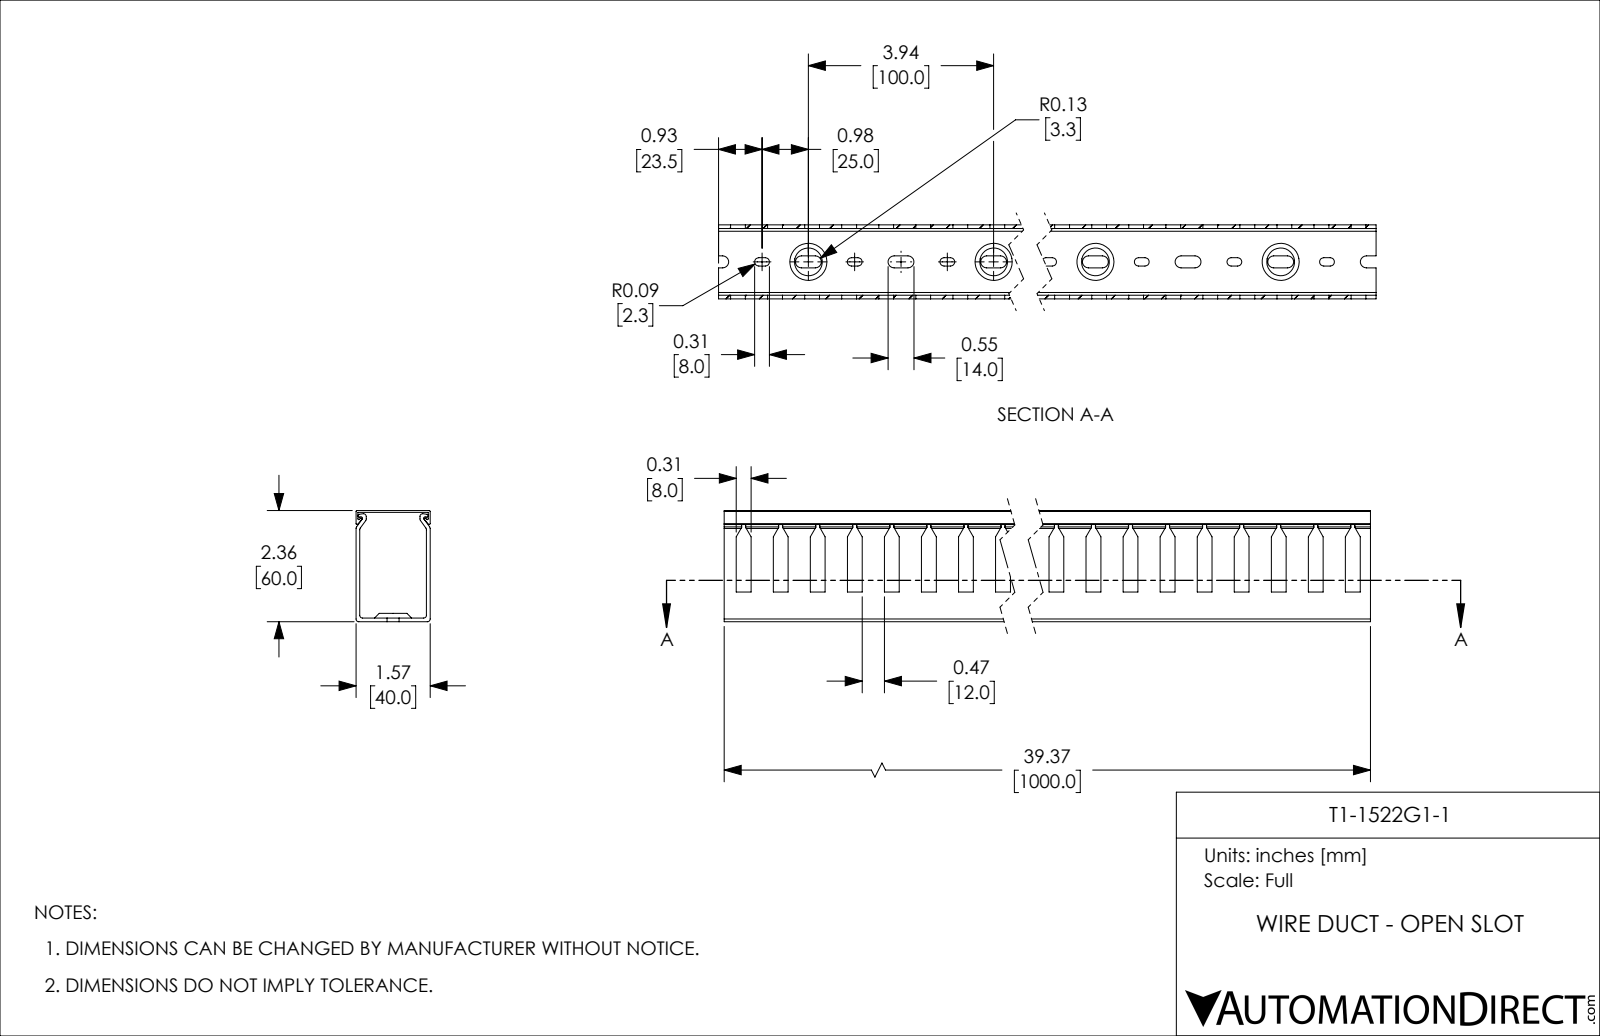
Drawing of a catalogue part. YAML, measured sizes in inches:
part_name: "T1-1522G1-1"
step_written_by: "SolidWorks 2021 (CONFIG_CONTROL_DESIGN)"
units: inches
bodies: {solids: 2, faces: 775, planar: 444, cylindrical: 311, other: 20}
overall_size: [39.37, 2.362, 1.575]
volume: 22.1
surface_area: 654.8
partial_cylinders:
  - {radius: 0.089, count: 40}
  - {radius: 0.128, count: 40}
  - {radius: 0.059, count: 12}
  - {radius: 0.02, count: 8}
  - {radius: 0.03, count: 6}
face_to_face_distances: [0.079, 1.496, 1.575, 0.039, 1.417, 2.362, 2.323, 2.244, 2.283, 1.535]
